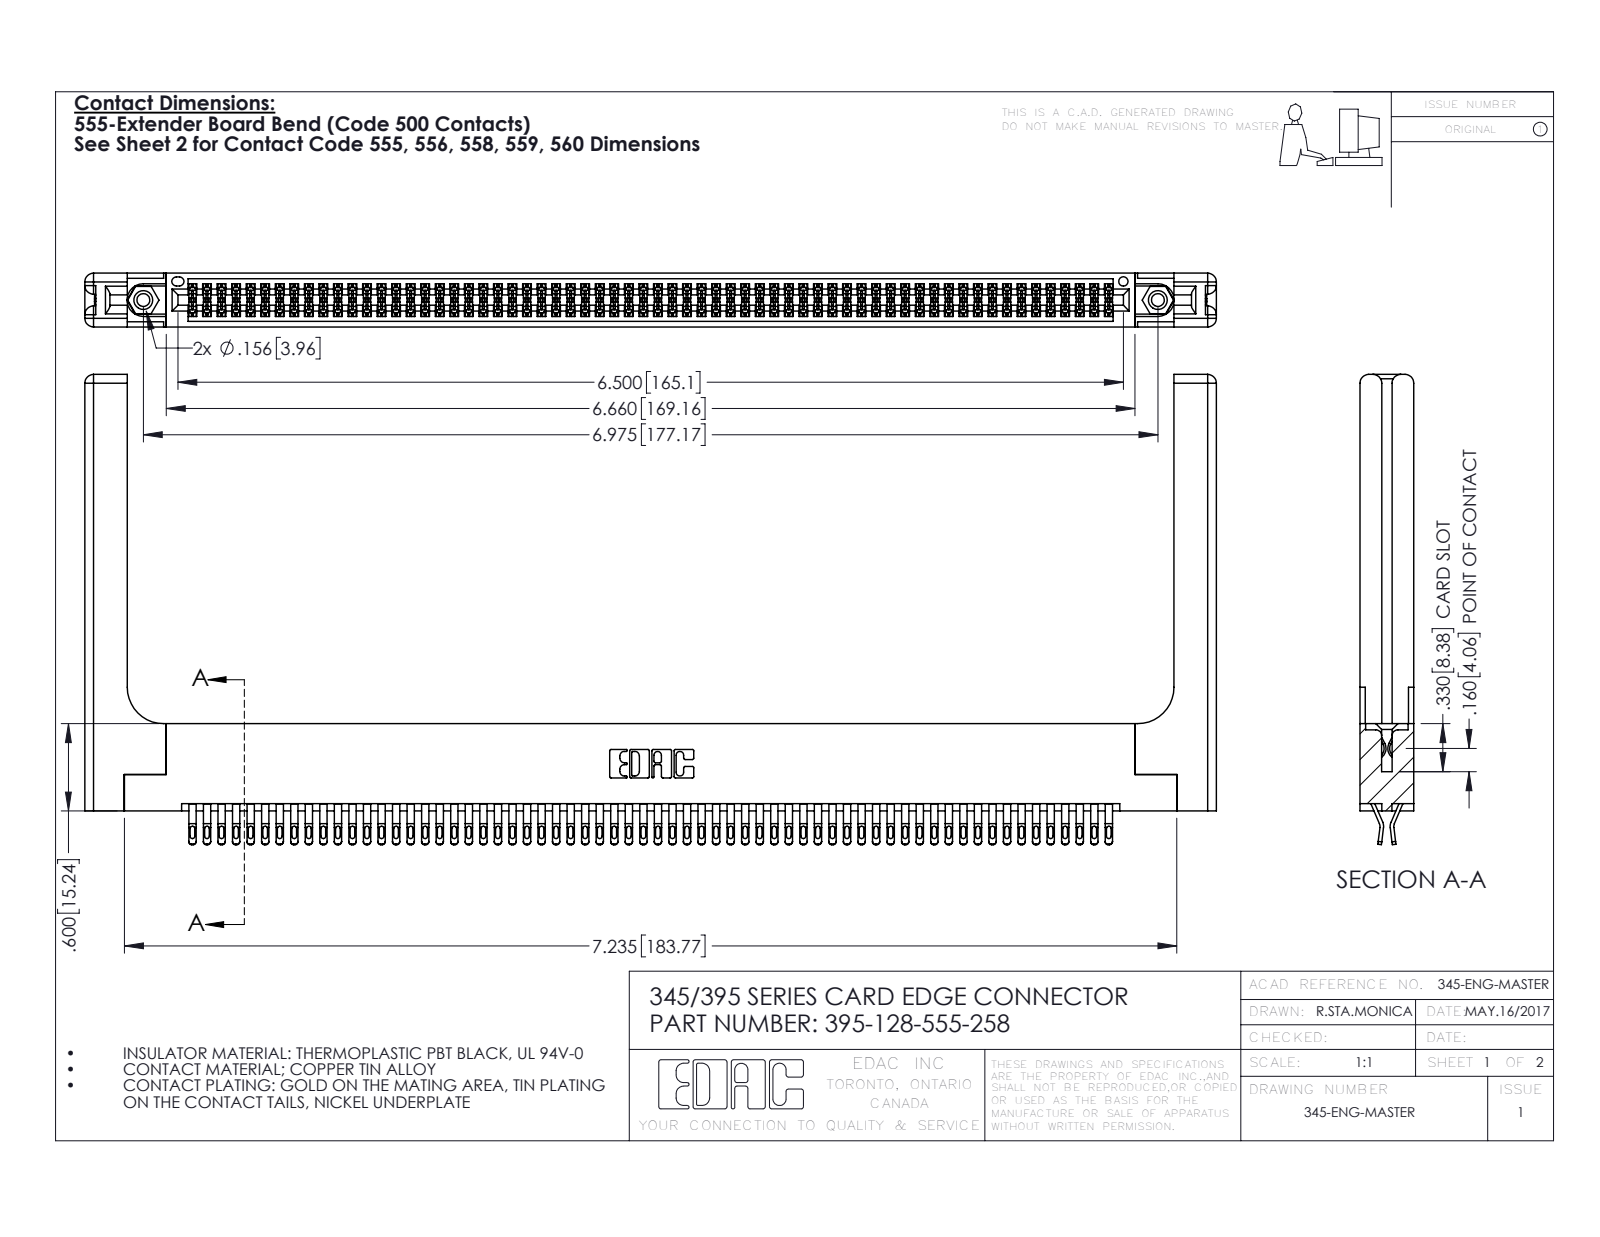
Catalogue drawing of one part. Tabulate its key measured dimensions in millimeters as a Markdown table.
| quantity | value |
| --- | --- |
| part name | 345-250-001_345-250-001-102; 345 Part_Flush Mounting Lugs - 0.156 Dia-TH; 345-220-058_345-220-058; 345-292-001_555 Tail (+1 more) |
| STEP written by | SolidWorks 2016 (CONFIG_CONTROL_DESIGN) |
| units | millimeters |
| bodies | 133 solids, 7550 faces (4196 planar, 3294 cylindrical, 60 other) |
| overall size | 197.6 × 82.1 × 9.4 |
| volume | 28 250 mm³ |
| surface area | 36 000 mm² |
| round holes (diameter × count) | 2.3 × 2, 3.2 × 2, 4 × 2, 1.6 × 1 |
| round bosses / shafts (diameter × count) | 3.9 × 2 |
| partial cylindrical surfaces (radius × count) | 0.4 × 320, 0.5 × 256, 0.2 × 192, 0.3 × 22, 1.5 × 16, 0.2 × 6, 0.8 × 6, 0.7 × 3 |
| main face-to-face distances | 1.8, 7.6, 9.4, 0.6, 5.1, 2.5, 6.9, 5.7, 3.8, 3.8 |
| hole center spacings | 6.9, 171.2, 177.2 |
